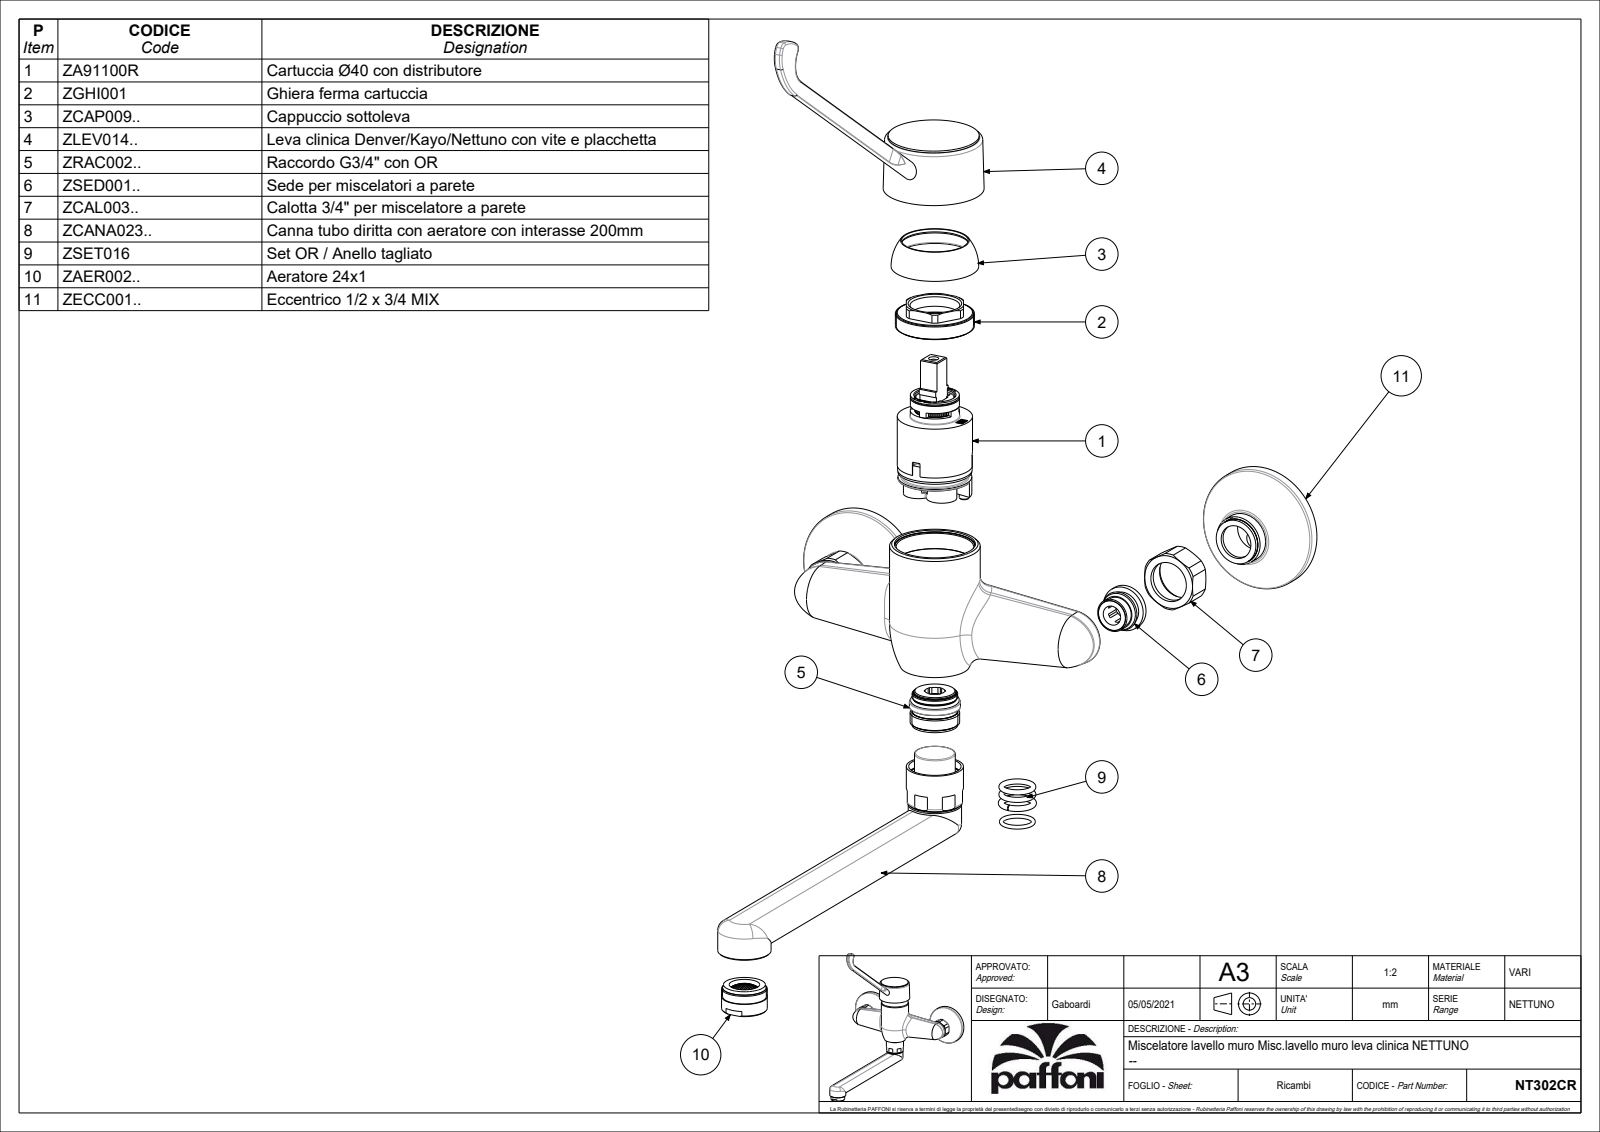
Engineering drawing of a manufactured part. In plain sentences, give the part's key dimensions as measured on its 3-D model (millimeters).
The part is named "NT302CR". Its 3-D file was written by "CREO PARAMETRIC BY PTC INC, 2020044 (CONFIG_CONTROL_DESIGN)". It is 6 solids with 3178 faces: 2235 planar, 495 cylindrical and 448 other. Overall it measures 268.5 by 257.28 by 215.5 millimeters. Its volume is 194 472 cubic millimeters and its surface area 165 508 square millimeters. Round holes: 4 of diameter 8, 2 of diameter 7, 2 of diameter 10.5, 2 of diameter 12, 2 of diameter 18, 2 of diameter 21, 2 of diameter 21.5, 2 of diameter 23, 2 of diameter 24.1, 2 of diameter 26, 2 of diameter 26.7, 2 of diameter 63.5. Round bosses or shafts: 3 of diameter 24, 2 of diameter 65.5, 2 of diameter 28.32, 2 of diameter 28, 2 of diameter 17.7, 2 of diameter 15.9, 2 of diameter 10, 2 of diameter 9.4. Partial cylindrical surfaces (rounded edges, fillets, slot ends): 69 of radius 0.5, 24 of radius 0.2, 8 of radius 0.3, 4 of radius 1.5, 3 of radius 7, 3 of radius 8, 3 of radius 15.5, 2 of radius 5.5. The main face-to-face distances are 1, 15, 16, 14, 1.5, 0.5, 4, 7.5, 2, 4.5. The hole center spacings are 2, 8.6, 9.9, 13.04, 14, 14.14, 14.76, 91.84.
